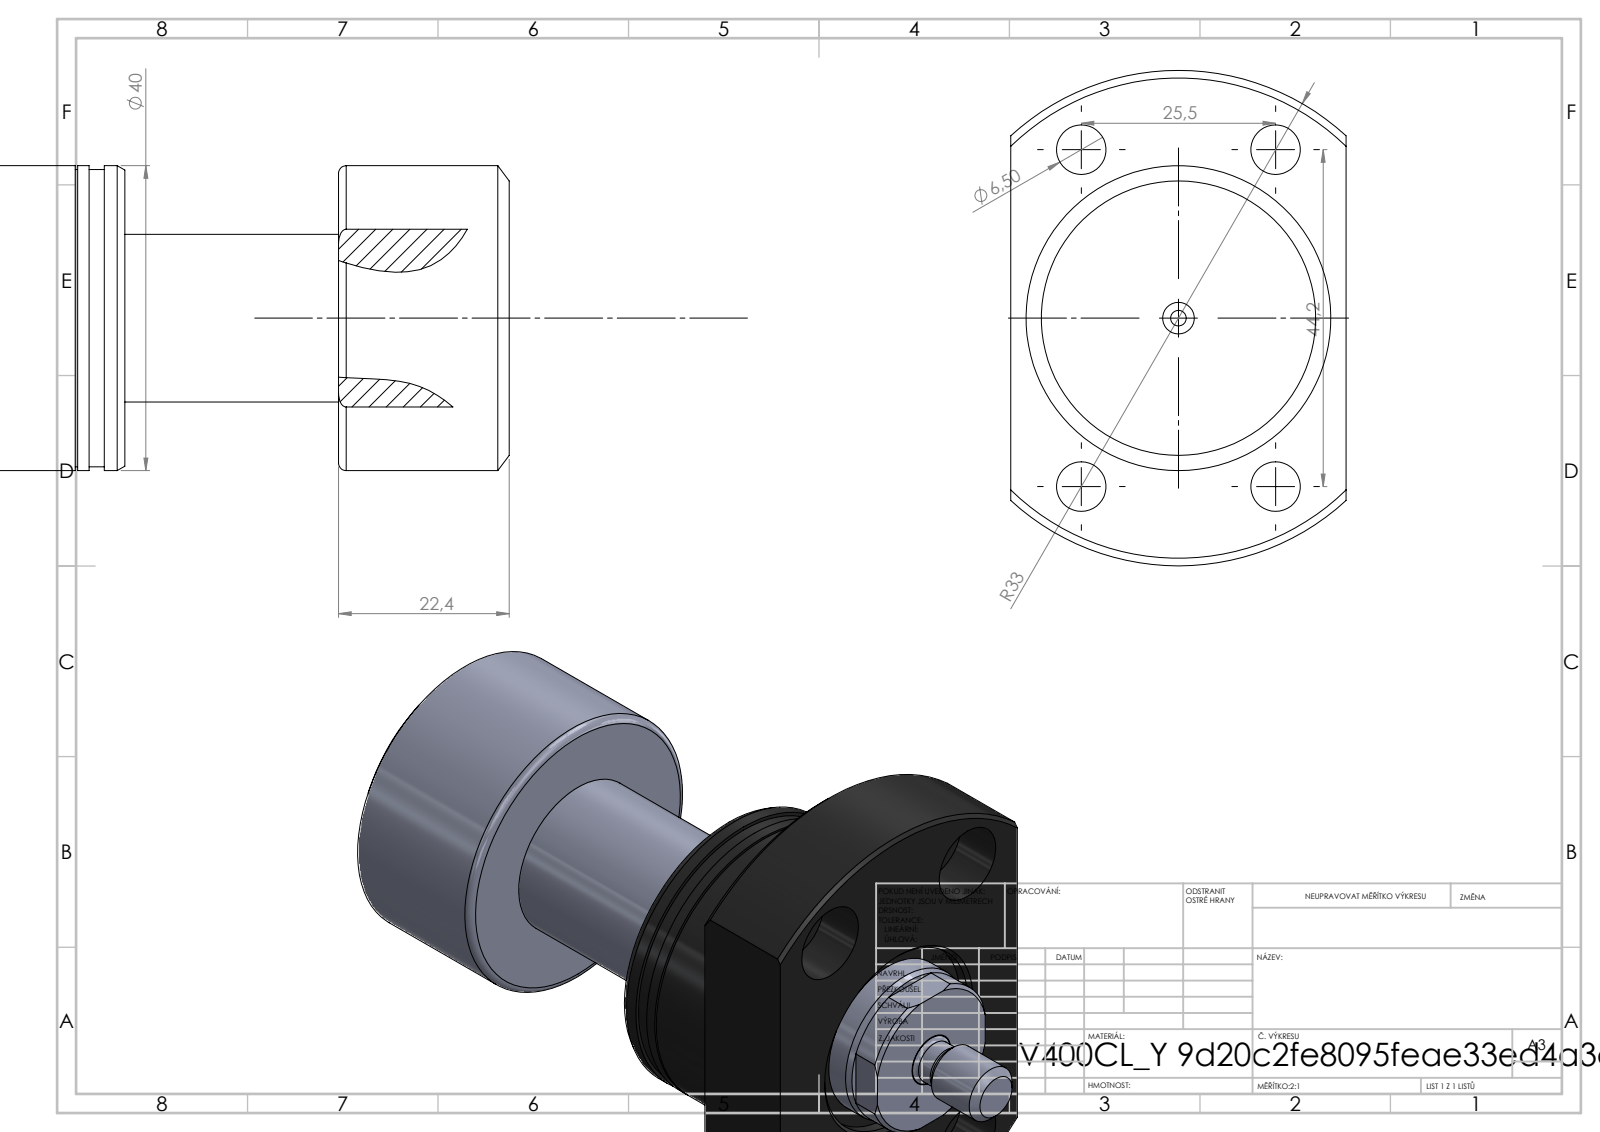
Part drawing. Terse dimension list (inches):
name: V400CL_PC_Y; V400CL_VC_X; MM
written by: SolidWorks 2019 (CONFIG_CONTROL_DESIGN)
unit: in
bodies: 3 solids, 117 faces (28 planar, 51 cylindrical, 38 other)
size: 3.937 × 2.559 × 1.732
volume: 5.83 in³; area: 36.02 in²
holes: 4× ⌀0.256, 4× ⌀0.413, 1× ⌀0.081, 1× ⌀0.197, 1× ⌀0.236, 1× ⌀0.866, 1× ⌀1.043
bosses: 1× ⌀1.575, 1× ⌀1.535, 1× ⌀0.314, 1× ⌀0.235
rounds: 1× R0.423, 1× R1.28
face distances: 0.551, 2.675, 3.226, 0.882, 1.793, 2.344, 1.986, 1.104, 0.689, 1.24
hole spacings: 1.004, 1.004, 1.74, 2.009
